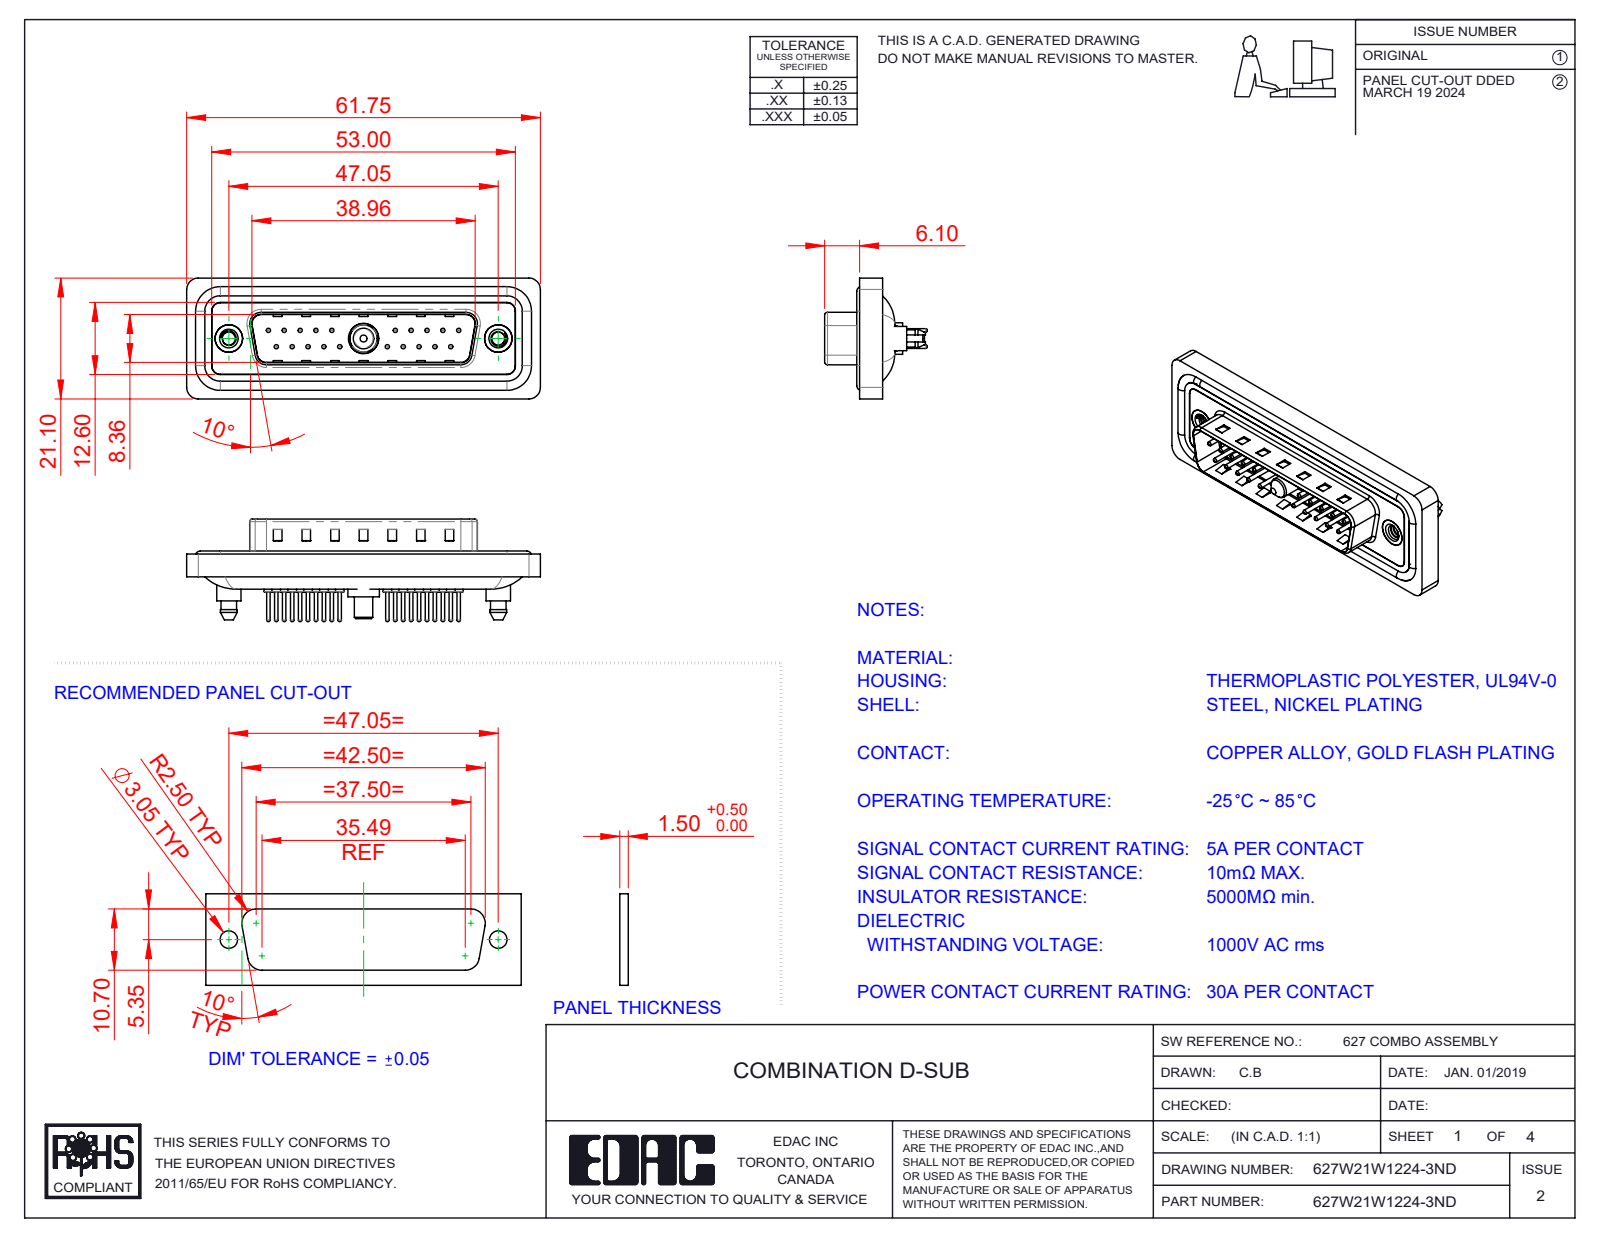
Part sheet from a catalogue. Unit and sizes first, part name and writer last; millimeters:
Units: millimetres
Overall size (bounding box): 61.75 × 21.1 × 17.9
Round holes (diameter × count): ⌀0.75 ×20, ⌀1.6 ×20, ⌀2 ×20, ⌀2.26 ×2, ⌀4 ×2, ⌀4.8 ×2, ⌀5 ×2, ⌀4.85 ×1, ⌀5.3 ×1
Round bosses / shafts (diameter × count): ⌀1.5 ×20, ⌀0.6 ×20, ⌀1.6 ×4, ⌀5.4 ×2, ⌀4.9 ×2, ⌀4.25 ×2, ⌀5.5 ×1, ⌀5.2 ×1
Partial cylindrical surfaces — rounded edges, fillets, slot ends (radius × count): R1.5 ×24, R2 ×18, R1.6 ×10, R0.5 ×8, R0.25 ×4, R0.6 ×4, R0.65 ×4, R0.9 ×4
Main face-to-face distances: 0.4, 1.5, 1.1, 1.6, 0.5, 3.1, 2.9, 4.1, 0.82, 9.58
Hole centre spacings: 3.16, 2.77, 5.54, 8.31, 5.04, 19.39, 20.97, 22.16
Volume: 7 339 mm³ · Surface area: 12 294 mm²
Bodies: 29 solids, 1320 faces (375 planar, 527 cylindrical, 418 other)
Part name (STEP PRODUCT): 627Combo Waterproof Housing_25 Contacts; 627Combo Shell Front_25 Contacts; Power Pin_30A S; 627Combo Threaded Boardlock_5 (+6 more)
STEP written by: SolidWorks 2023 (CONFIG_CONTROL_DESIGN)
